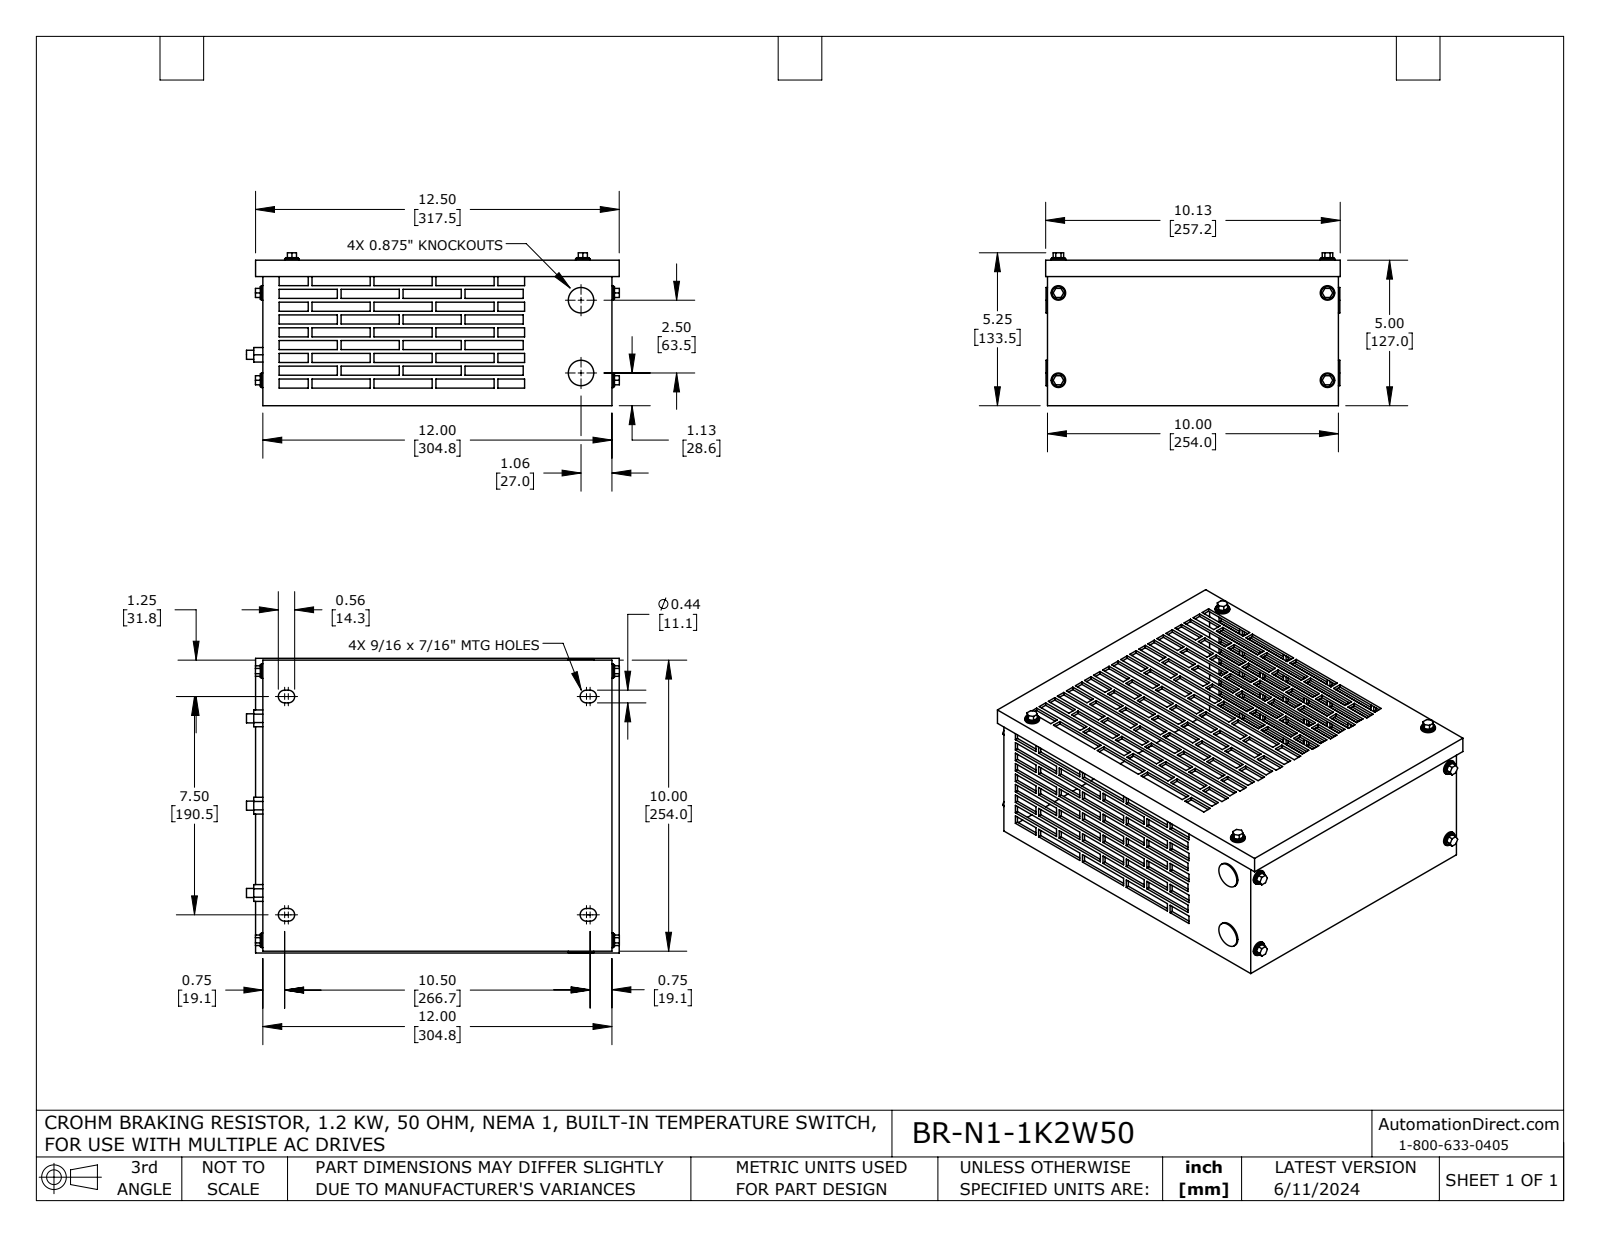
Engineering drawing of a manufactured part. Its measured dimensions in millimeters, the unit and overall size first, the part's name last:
Units: millimetres
Overall size (bounding box): 325.6 × 257.2 × 133.5
Round holes (diameter × count): ⌀6.4 ×8, ⌀19.1 ×2
Round bosses / shafts (diameter × count): ⌀12.7 ×8, ⌀11.1 ×8, ⌀8 ×3, ⌀22.2 ×2
Partial cylindrical surfaces — rounded edges, fillets, slot ends (radius × count): R5.6 ×8
Main face-to-face distances: 2.5, 124.5, 302.3, 127, 121.9, 251.5, 304.8, 299.7, 254, 248.9
Hole centre spacings: 235, 76.2, 247, 254, 346, 63.5
Volume: 611 600 mm³ · Surface area: 533 000 mm²
Bodies: 32 solids, 981 faces (879 planar, 102 cylindrical, 0 other)
Part name (STEP PRODUCT): BR-N1-1K2W50
STEP written by: SolidWorks 2021 (AUTOMOTIVE_DESIGN)
